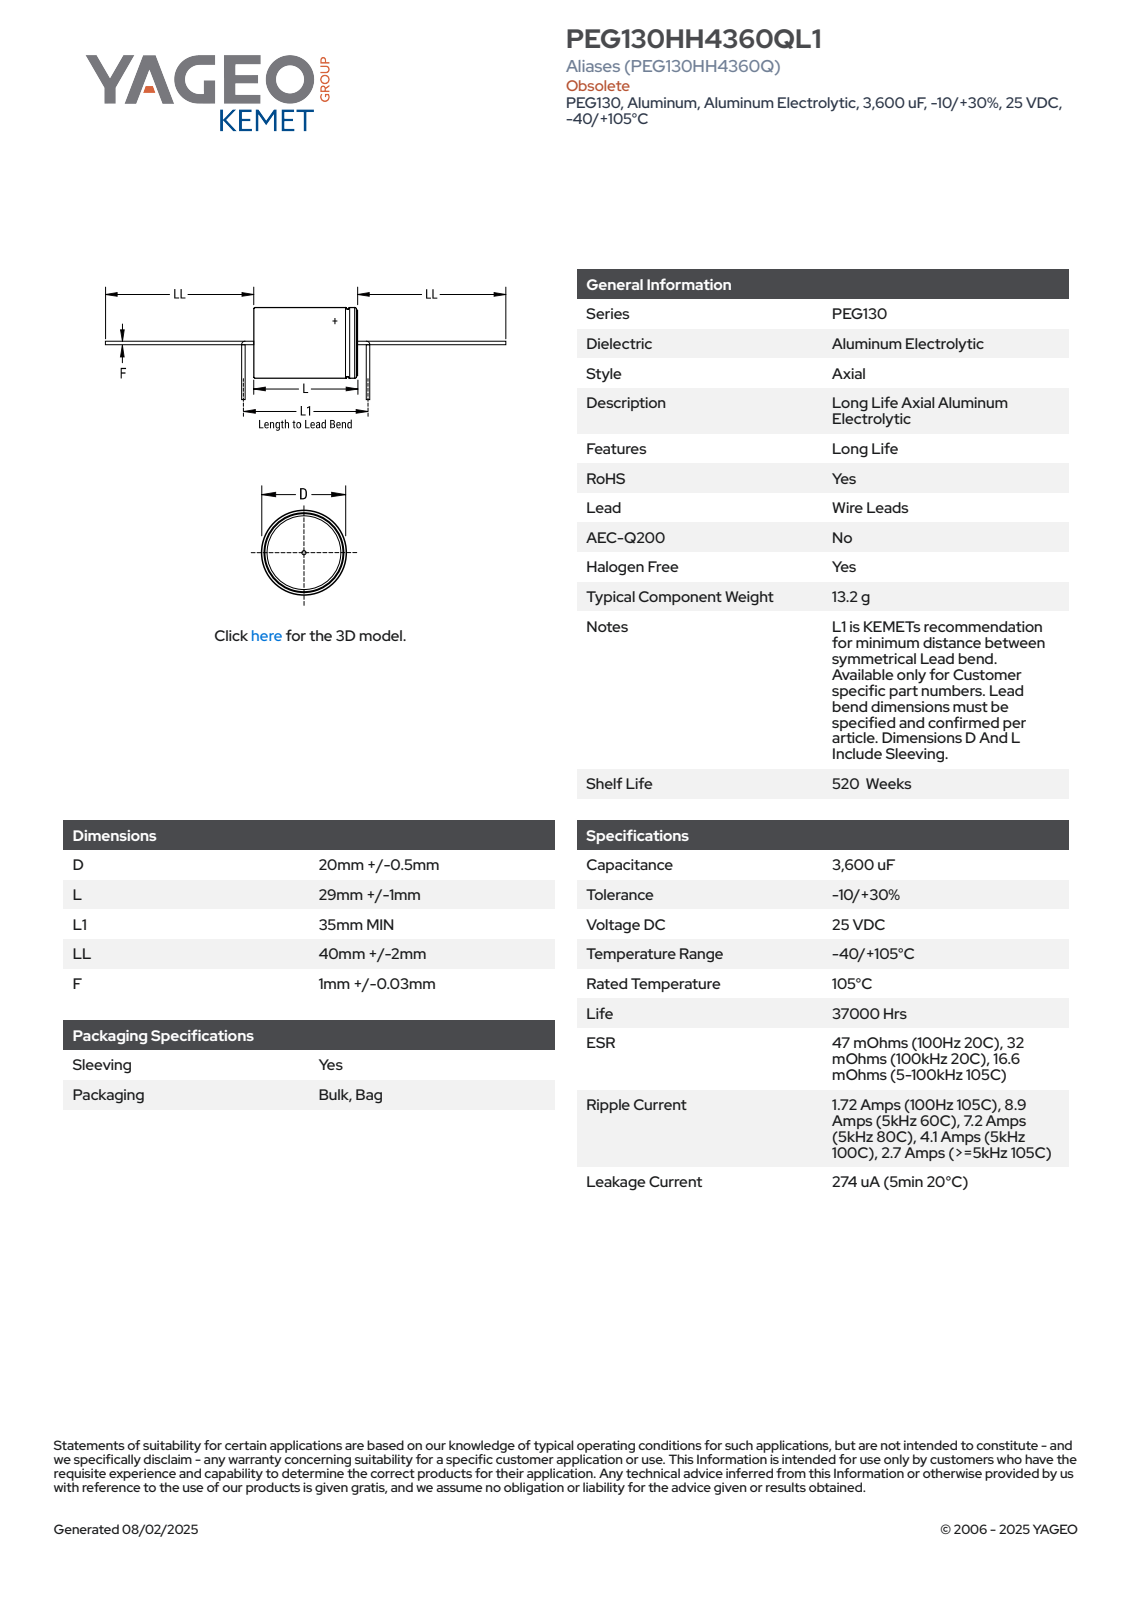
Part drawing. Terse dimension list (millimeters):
name: CAA_PEG124_20X29_D20.5L30LL42F1.03
written by: SolidWorks 2014 (AUTOMOTIVE_DESIGN)
unit: mm
bodies: 1 solid, 99 faces (27 planar, 29 cylindrical, 43 other)
size: 114 × 20.5 × 20.5
volume: 9 664 mm³; area: 2 933 mm²
holes: 1× ⌀19.5
bosses: 1× ⌀20.5, 1× ⌀20, 1× ⌀1.03
rounds: 1× R10.24
face distances: 29, 30, 1, 42, 72, 71, 114, 43
